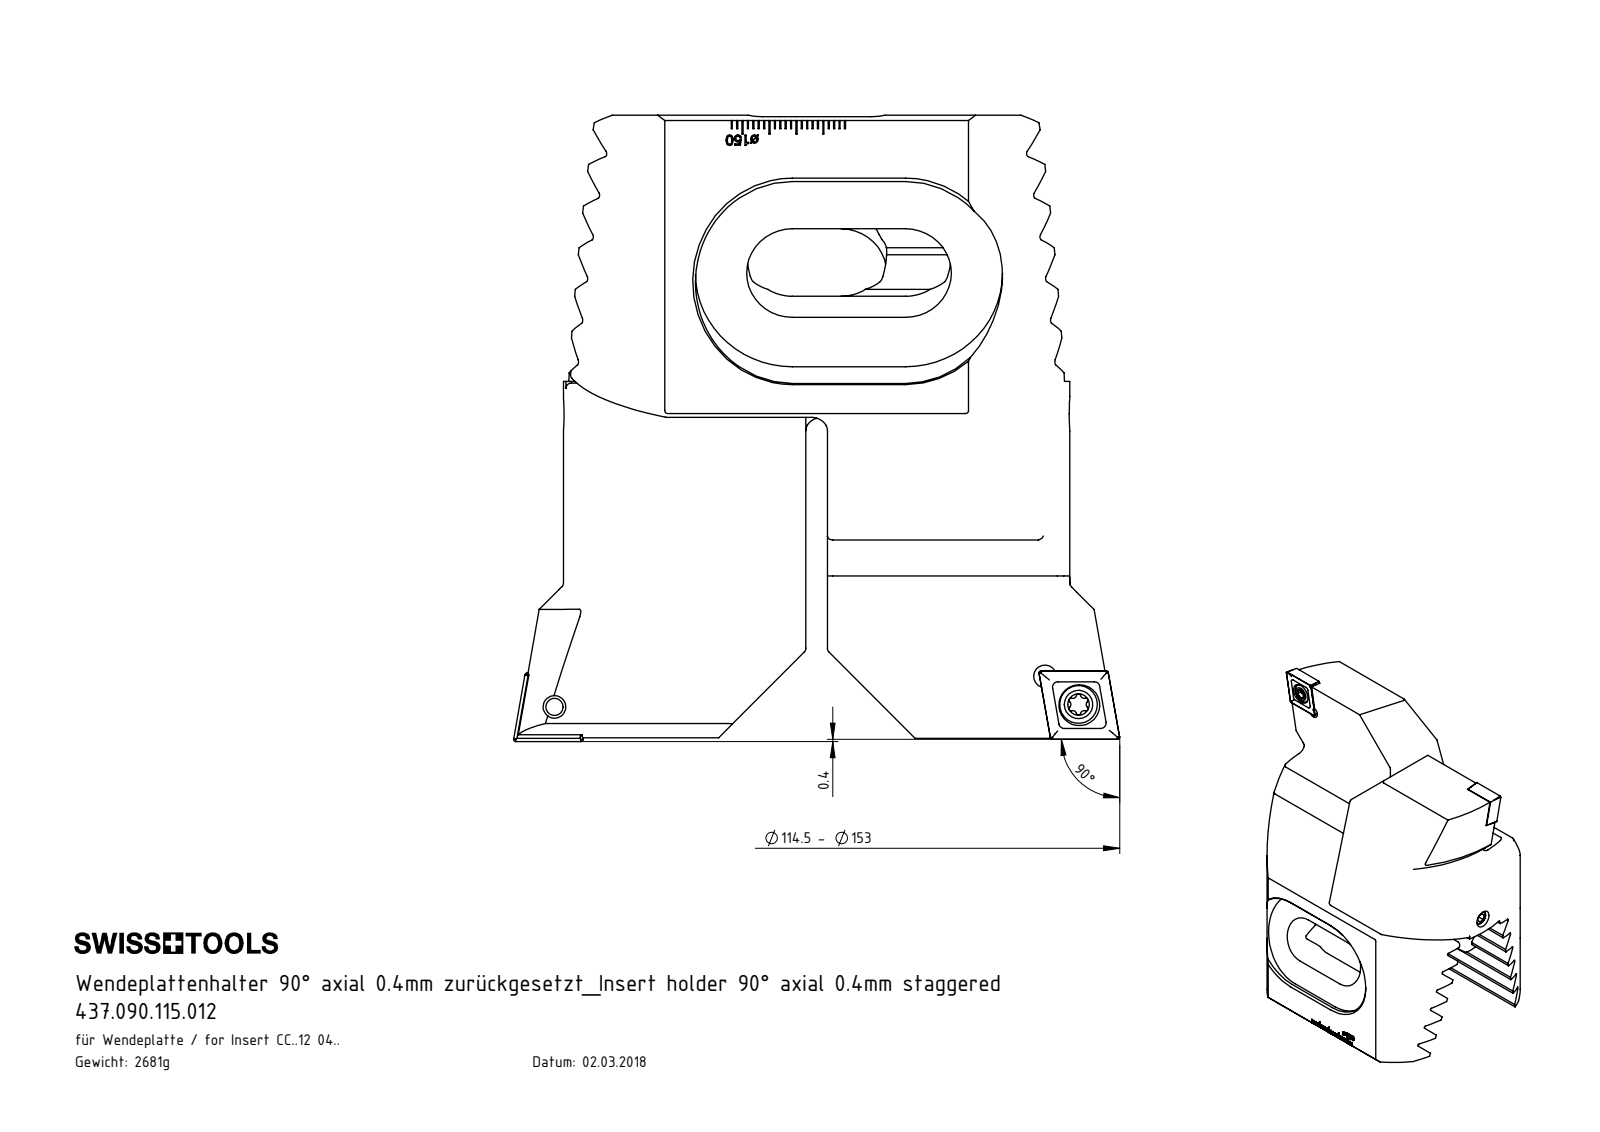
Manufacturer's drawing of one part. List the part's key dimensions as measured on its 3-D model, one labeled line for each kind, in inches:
Part name (STEP PRODUCT): Z94-WCC.004.067_einzeln; 437.090.115.012; Z94-ER3.001.040; Z94-WCC.001.067_Ersatzteile (+4 more)
STEP written by: SolidWorks 2017 (CONFIG_CONTROL_DESIGN)
Units: inches
Bodies: 8 solids, 796 faces (446 planar, 139 cylindrical, 211 other)
Overall size (bounding box): 4.559 × 4.429 × 2.961
Volume: 20.96 in³ · Surface area: 99.92 in²
Round holes (diameter × count): ⌀0.079 ×4, ⌀0.165 ×4, ⌀0.217 ×2, ⌀0.299 ×2, ⌀0.197 ×1
Round bosses / shafts (diameter × count): ⌀0.276 ×2, ⌀0.197 ×2, ⌀0.236 ×1, ⌀0.157 ×1
Partial cylindrical surfaces — rounded edges, fillets, slot ends (radius × count): R0.039 ×16, R0.015 ×12, R0.023 ×12, R0.027 ×6, R0.027 ×6, R0.118 ×6, R0.335 ×4, R0.709 ×4
Main face-to-face distances: 0.273, 0.818, 0.546, 0.545, 0.272, 0.519, 1.469, 1.492, 1.091, 0.063
Hole centre spacings: 0.157, 0.328, 0.984, 0.315, 0.32, 0.323, 0.996, 1.033
